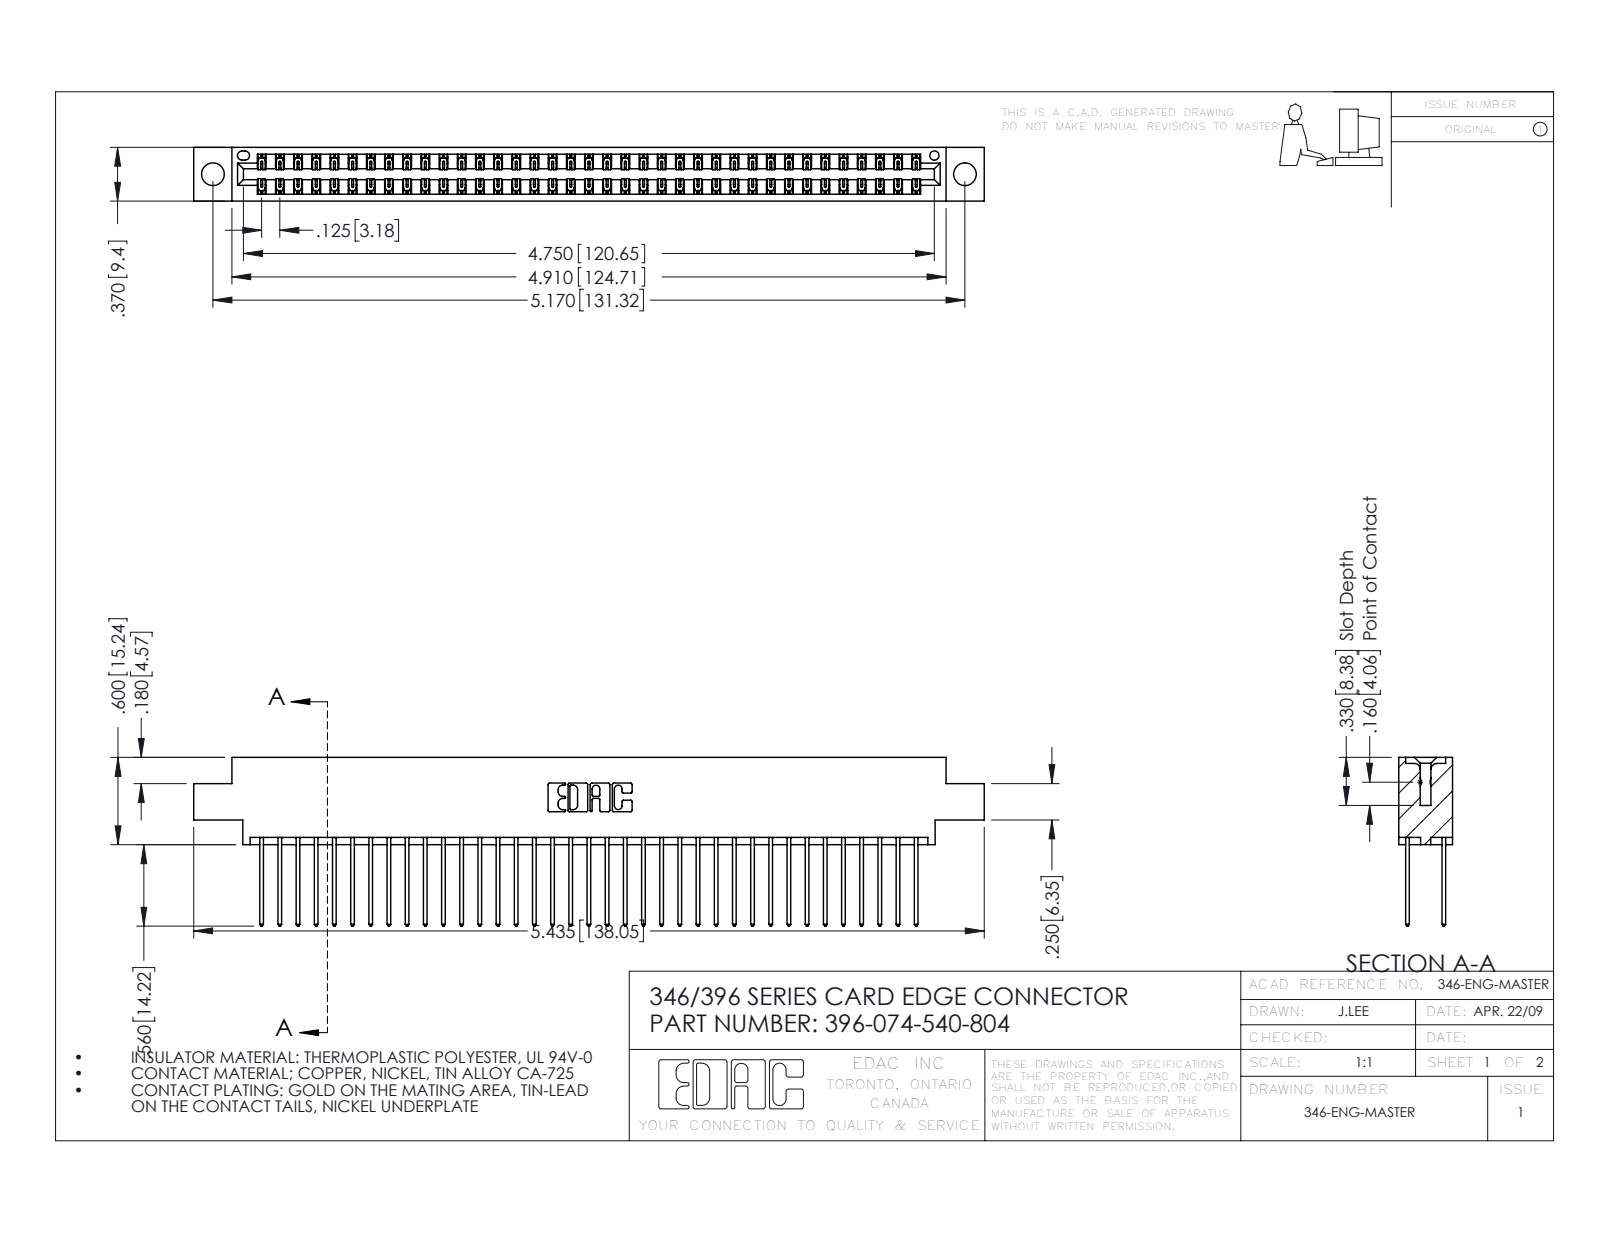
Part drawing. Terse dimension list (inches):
name: 346 Part_0.170 Offset - 0.156 Dia-TH; 345-292-001_345-293-140; 396-074-540-804
written by: SolidWorks 2016 (CONFIG_CONTROL_DESIGN)
unit: in
bodies: 75 solids, 3974 faces (2670 planar, 1304 cylindrical, 0 other)
size: 5.435 × 1.16 × 0.37
volume: 0.821 in³; area: 30.6 in²
holes: 2× ⌀0.156, 1× ⌀0.064
rounds: 111× R0.006, 74× R0.01, 22× R0.01, 6× R0.007, 6× R0.031, 3× R0.026, 2× R0.014, 2× R0.022
face distances: 0.048, 0.322, 0.25, 0.072, 0.298, 0.025, 0.37, 0.275, 0.148, 0.222
hole spacings: 0.246, 4.961, 5.17
